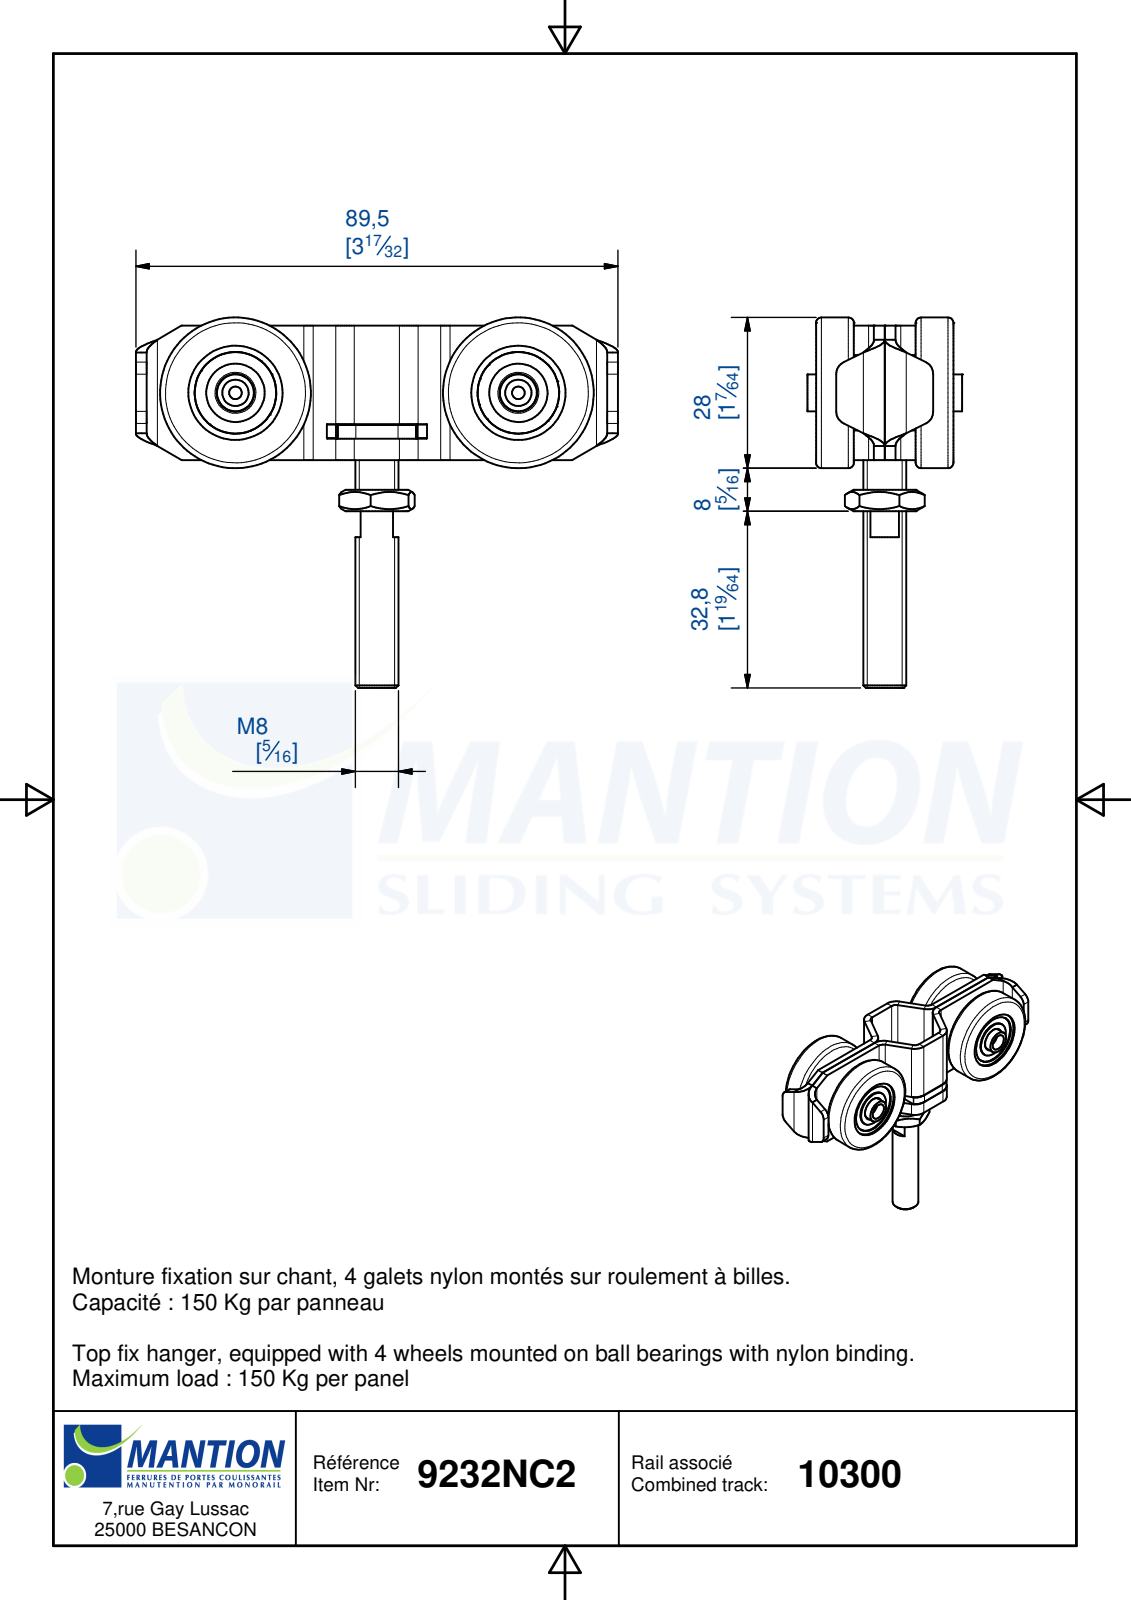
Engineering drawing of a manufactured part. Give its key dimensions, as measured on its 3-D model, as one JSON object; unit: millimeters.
{"part_name": "9232NC2; 23767; 23765; 23766 (+8 more)", "step_written_by": "Autodesk Inventor 2019 (AUTOMOTIVE_DESIGN)", "units": "millimeters", "bodies": {"solids": 20, "faces": 515, "planar": 249, "cylindrical": 147, "other": 119}, "overall_size": [89.54, 68.8, 28.7], "volume_mm3": 31392, "surface_area_mm2": 32878, "round_holes": [[4.9, 2], [7, 2], [7.1, 2], [15.16, 2], [17.5, 2], [19, 2], [6.65, 1], [8.2, 1], [8.3, 1]], "round_bosses_or_shafts": [[28, 2], [15.14, 2], [14, 2], [10.84, 2], [6.85, 2], [16, 1], [8, 1]], "partial_cylinders_radius": [[0.2, 20], [2, 12], [4, 12], [2.5, 4], [4.5, 4], [9.8, 1]], "face_to_face_distances": [2, 6.5, 18.5, 4, 4.25, 0.5, 12, 6.25, 14.75, 5.75], "hole_center_spacings": [52.54]}
